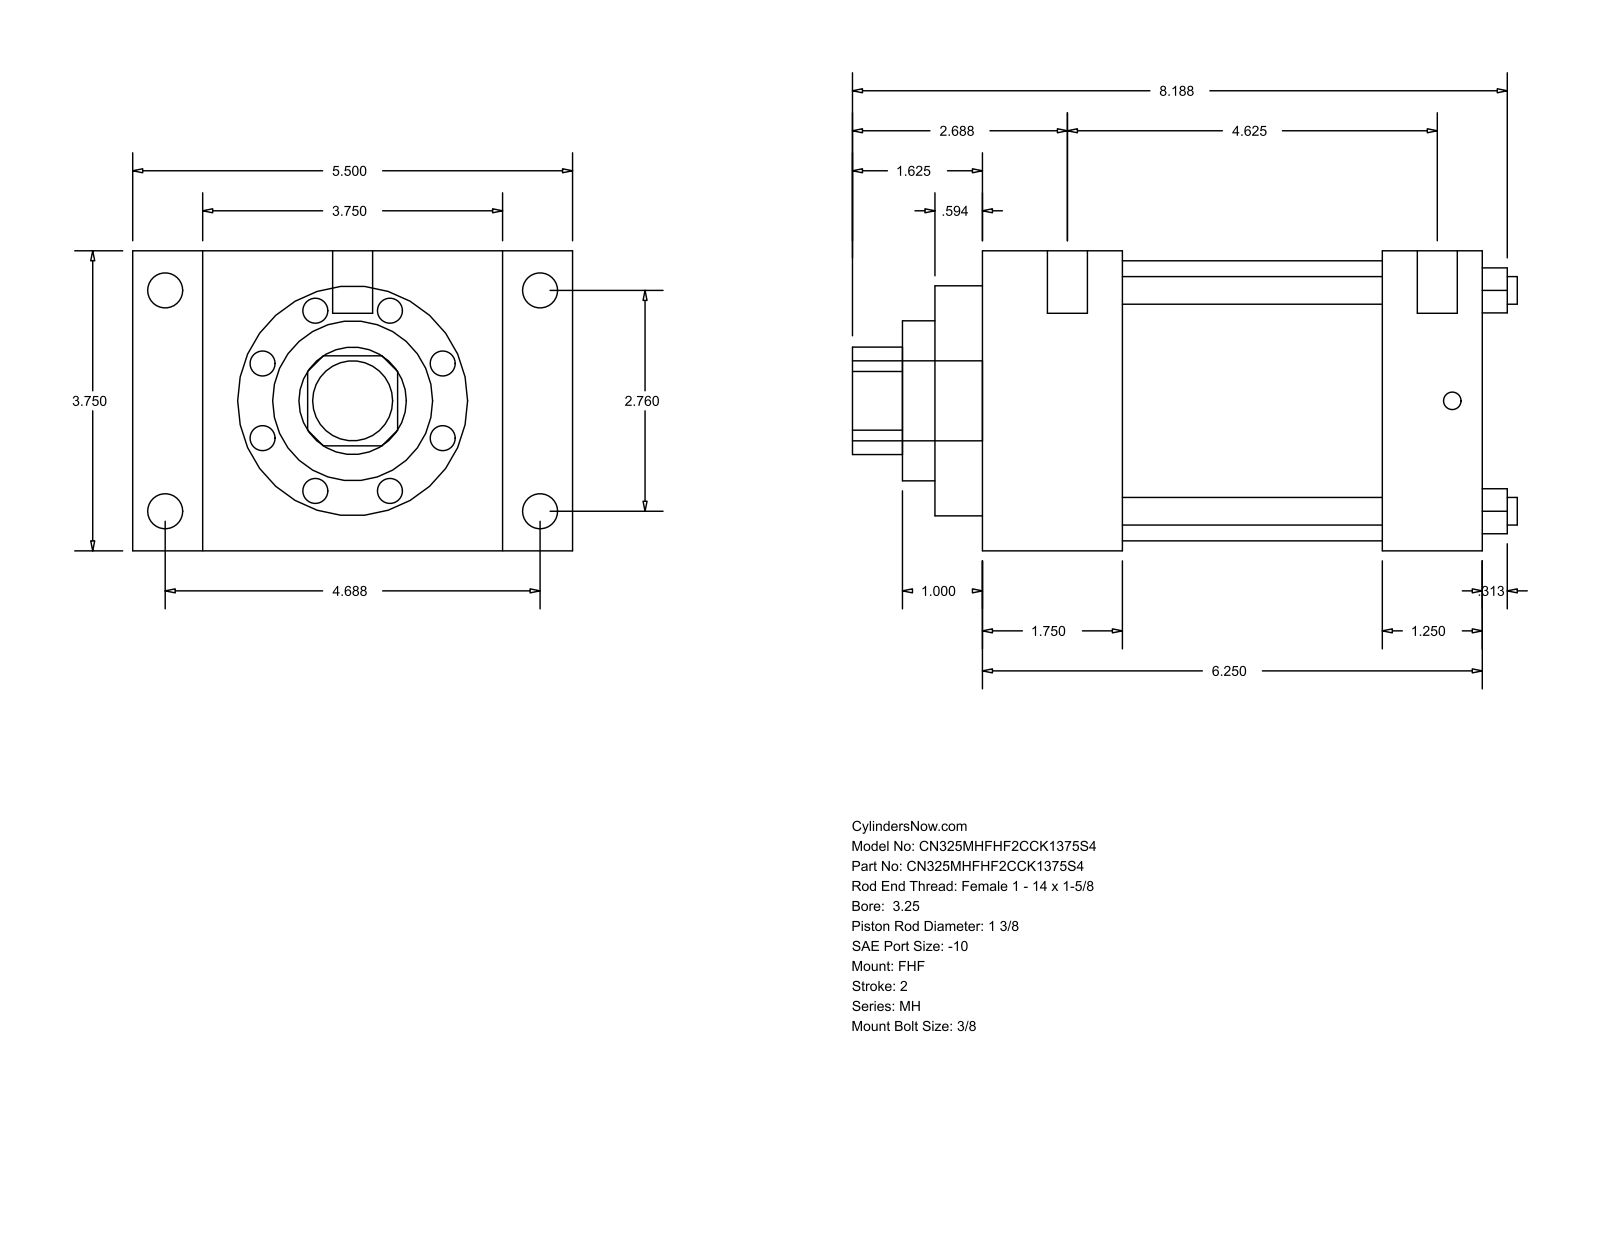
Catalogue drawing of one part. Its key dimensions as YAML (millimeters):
part_name: "MH_FHF__0325_1.375"
step_written_by: "GSSL Pune (CONFIG_CONTROL_DESIGN)"
units: millimeters
bodies: {solids: 0, faces: 90, planar: 61, cylindrical: 29, other: 0}
overall_size: [211.14, 139.7, 95.25]
round_holes:
  - {diameter: 8.76, count: 4}
  - {diameter: 34.92, count: 1}
  - {diameter: 50.8, count: 1}
  - {diameter: 73.03, count: 1}
  - {diameter: 88.9, count: 1}
round_bosses_or_shafts:
  - {diameter: 11.13, count: 4}
  - {diameter: 5.56, count: 4}
  - {diameter: 12.7, count: 2}
  - {diameter: 25.4, count: 1}
partial_cylinders:
  - {radius: 17.06, count: 1}
face_to_face_distances: [95.24, 158.76, 44.45, 114.31, 22.23, 117.47, 139.7, 127.01, 82.56, 31.75]
hole_center_spacings: [49.57, 70.1, 99.14]
